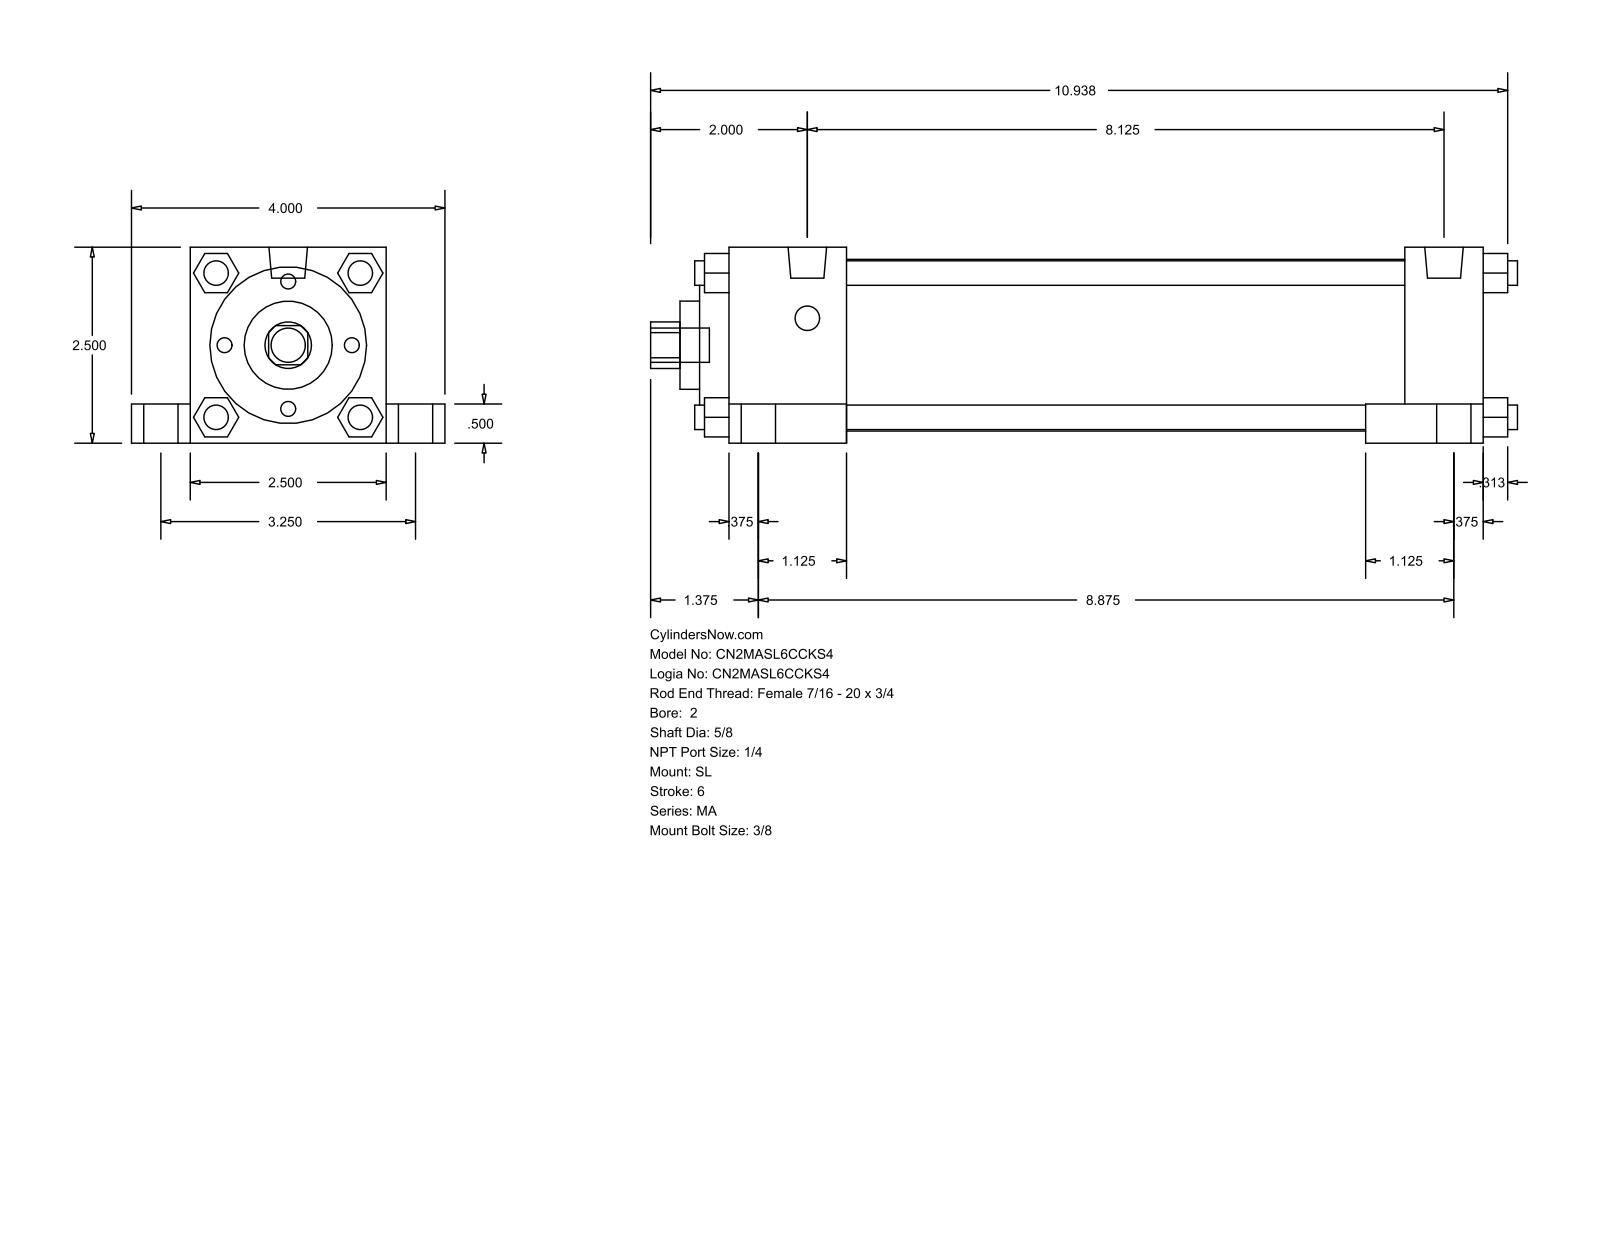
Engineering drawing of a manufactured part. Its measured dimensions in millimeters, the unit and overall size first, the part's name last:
Units: millimetres
Overall size (bounding box): 280.99 × 101.6 × 63.5
Round holes (diameter × count): ⌀15.88 ×1, ⌀28.57 ×1, ⌀50.8 ×1, ⌀55.63 ×1
Round bosses / shafts (diameter × count): ⌀7.94 ×8, ⌀11.11 ×5, ⌀17.46 ×4, ⌀12.49 ×2
Partial cylindrical surfaces — rounded edges, fillets, slot ends (radius × count): R7.54 ×1
Main face-to-face distances: 63.5, 12.7, 9.52, 180.97, 19.05, 82.55, 38.1, 50.8, 244.48, 206.38
Bodies: 0 solids, 150 faces (113 planar, 37 cylindrical, 0 other)
Part name (STEP PRODUCT): MA_SL__0200_0.625
STEP written by: GSSL Pune (CONFIG_CONTROL_DESIGN)
